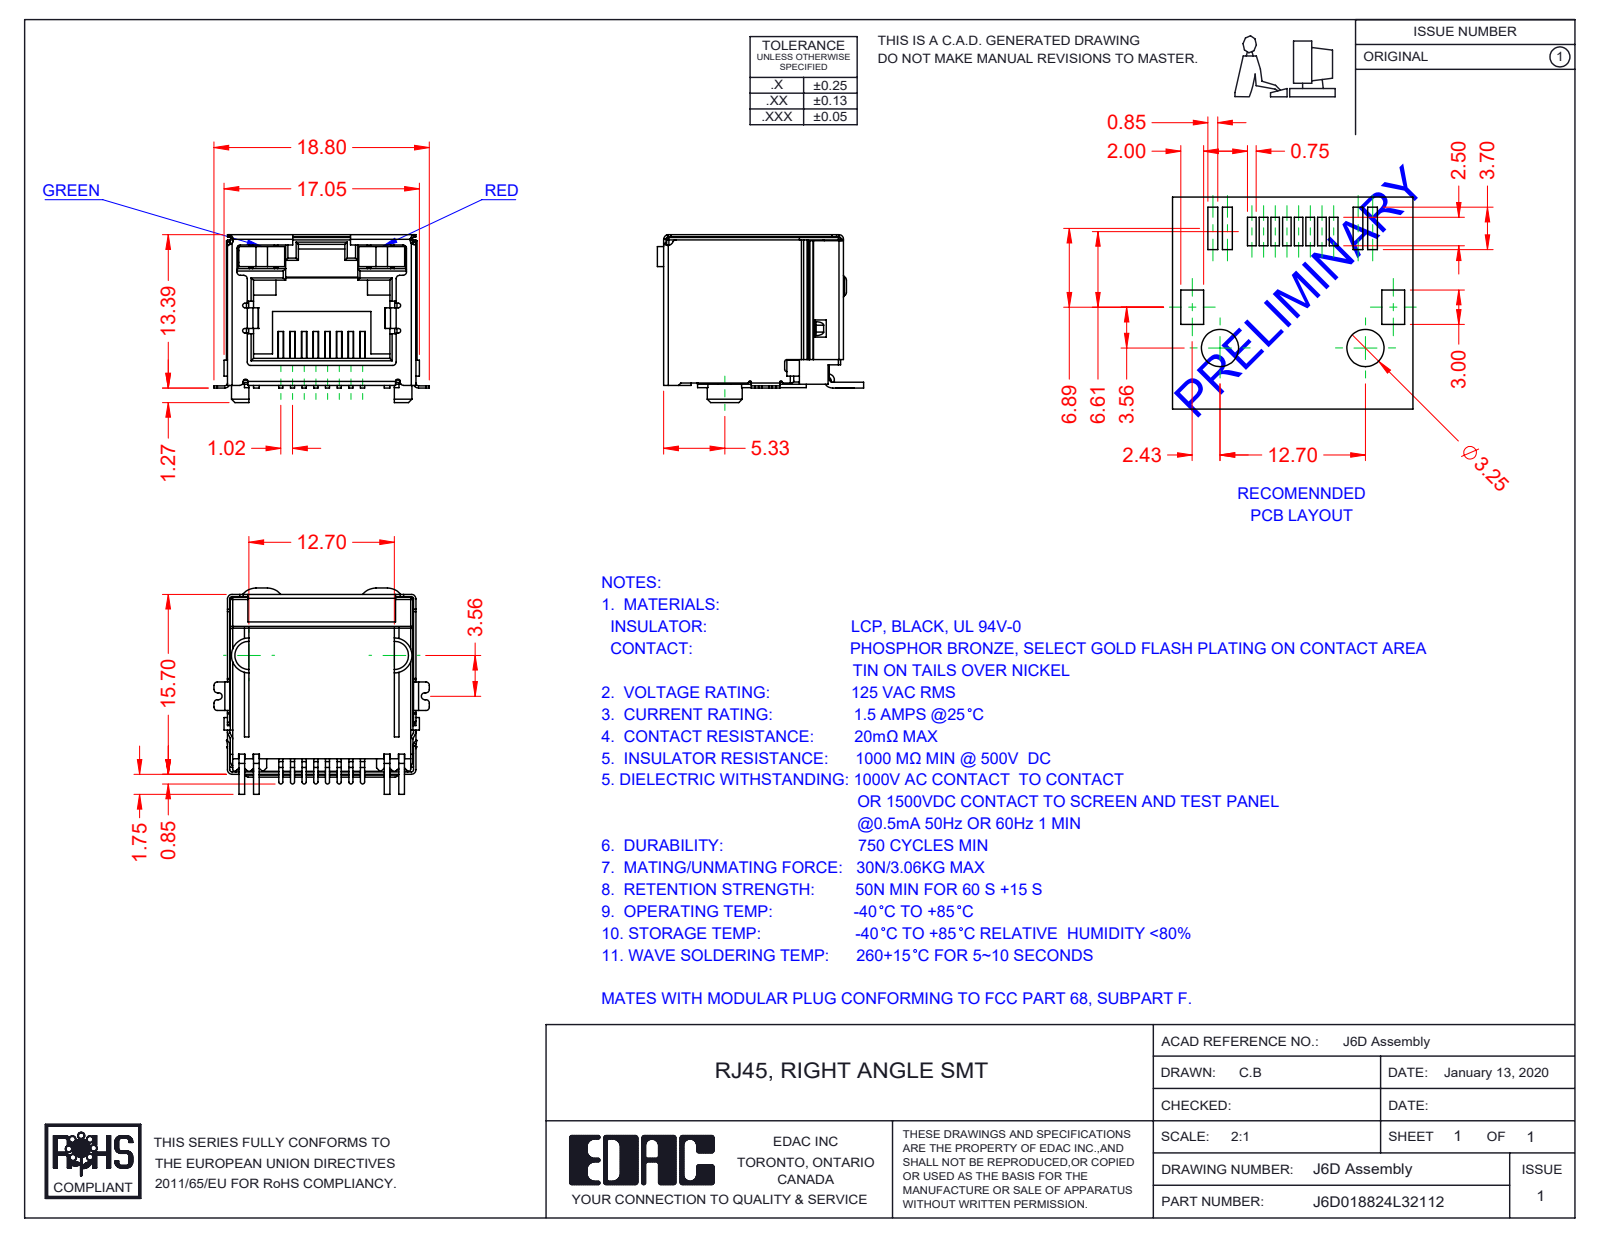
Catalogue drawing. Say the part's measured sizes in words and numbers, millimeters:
The part is named "6D LED RH_2-Red; 6D Contacts; J6D018824L32112; 6D Shield_LED - No EMI (+2 more)". Its 3-D file was written by "SolidWorks 2016 (CONFIG_CONTROL_DESIGN)". It is 12 solids with 893 faces: 644 planar, 216 cylindrical and 33 other. Overall it measures 18.8 by 18 by 14.65 millimeters. Its volume is 1 804 cubic millimeters and its surface area 4 898 square millimeters. Partial cylindrical surfaces (rounded edges, fillets, slot ends): 39 of radius 0.3, 37 of radius 0.2, 16 of radius 0.4, 12 of radius 0.1, 8 of radius 0.15, 8 of radius 0.18, 6 of radius 0.5, 5 of radius 1.5. The main face-to-face distances are 16, 16.25, 16.2, 2.25, 1, 15.95, 16.05, 12.8, 0.45, 16.45.
